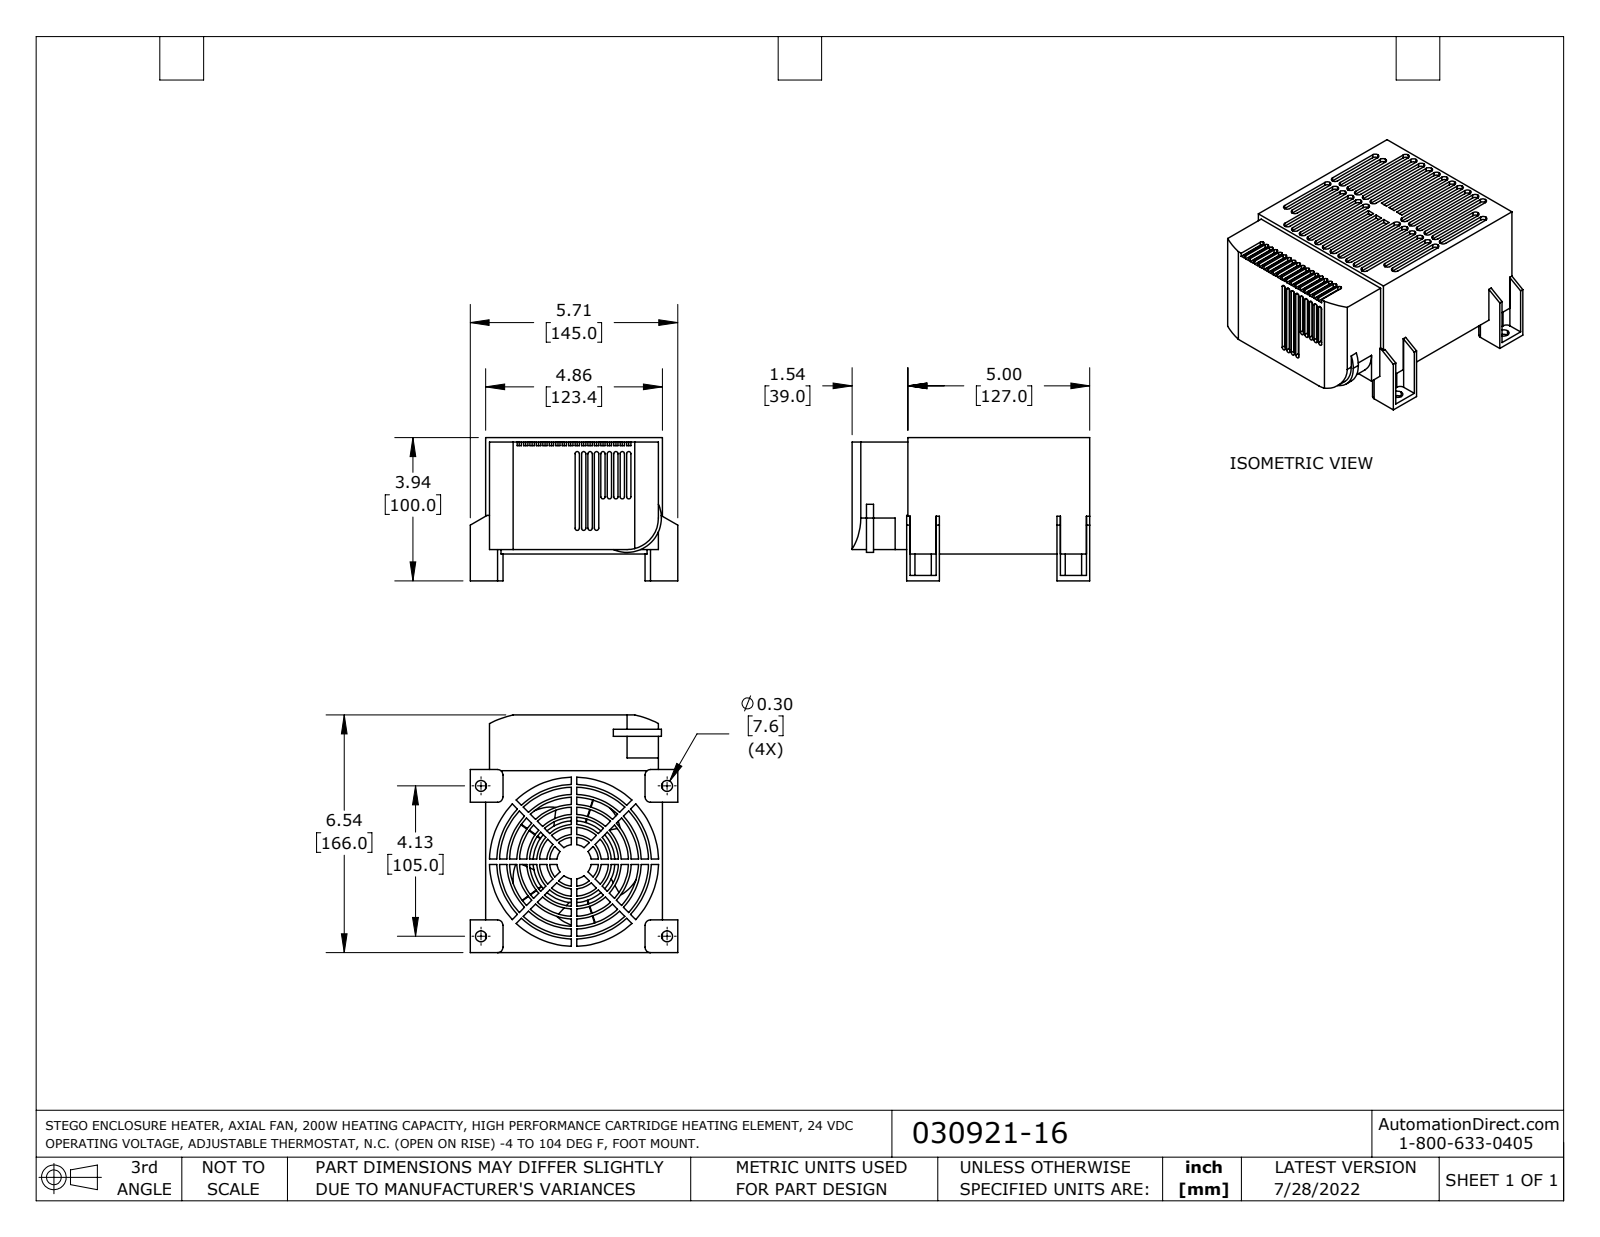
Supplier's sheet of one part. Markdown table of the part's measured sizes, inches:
| quantity | value |
| --- | --- |
| part name | 030921-16_Default |
| STEP written by | SolidWorks 2021 (CONFIG_CONTROL_DESIGN) |
| units | inches |
| bodies | 1 solid, 667 faces (438 planar, 229 cylindrical, 0 other) |
| overall size | 6.535 × 5.709 × 3.937 |
| volume | 84.42 in³ |
| surface area | 239.6 in² |
| round holes (diameter × count) | 0.3 × 4, 0.394 × 1, 1.35 × 1, 1.9 × 1, 2.45 × 1, 3 × 1, 3.55 × 1, 4.1 × 1, 4.65 × 1 |
| round bosses / shafts (diameter × count) | 4.25 × 1, 3.7 × 1, 3.15 × 1, 2.6 × 1, 2.25 × 1, 2.05 × 1, 1.5 × 1, 0.95 × 1 |
| partial cylindrical surfaces (radius × count) | 0.1 × 54, 0.059 × 36, 0.135 × 8, 0.15 × 8, 1.086 × 5, 2.756 × 2, 0.866 × 1, 0.945 × 1 |
| main face-to-face distances | 0.1, 4.86, 2.1, 0.124, 1, 3.1, 3.2, 2.2, 3.076, 0.4 |
| hole center spacings | 3.279, 3.3, 4.134, 5.118, 6.579 |
